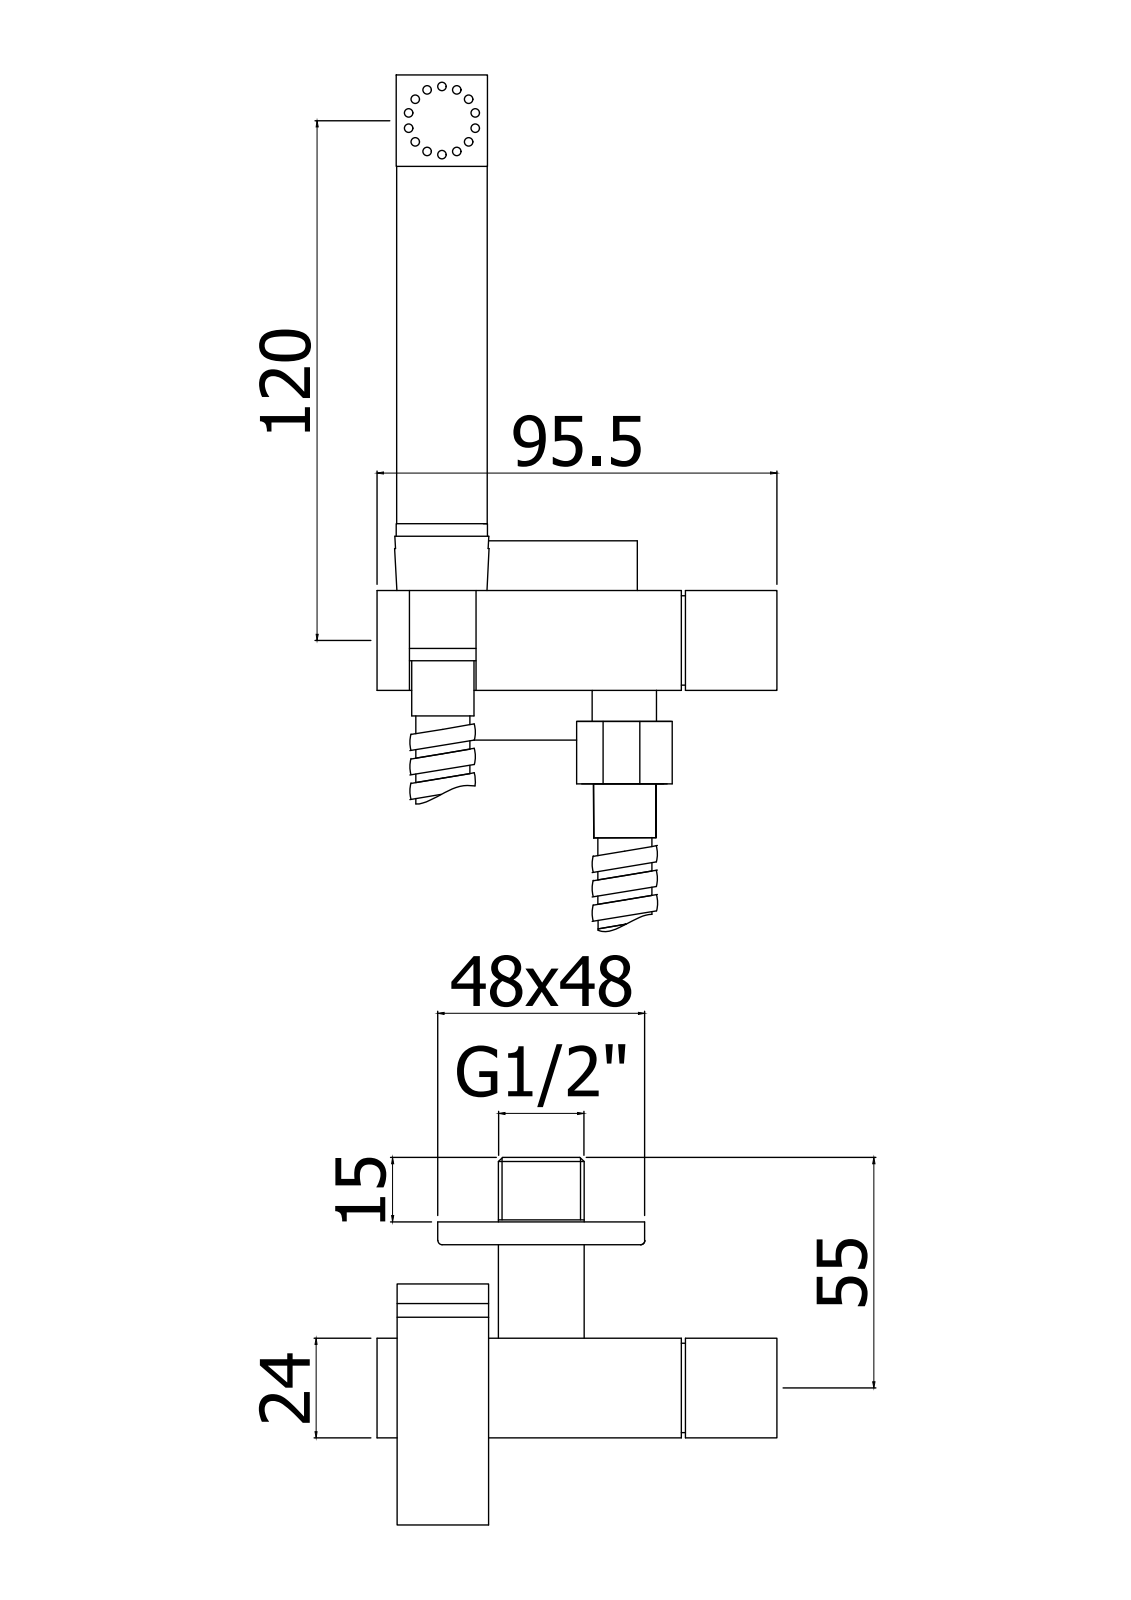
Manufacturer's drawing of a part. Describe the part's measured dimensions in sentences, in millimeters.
The part is named "ZDUP111CR". Its 3-D file was written by "CREO PARAMETRIC BY PTC INC, 2020044 (CONFIG_CONTROL_DESIGN)". It is 1 solid with 460 faces: 114 planar, 220 cylindrical and 126 other. Overall it measures 371 by 95.5 by 67.45 millimeters. Its volume is 171 674 cubic millimeters and its surface area 72 919 square millimeters. Round holes: 12 of diameter 1.2, 1 of diameter 10, 1 of diameter 15.5, 1 of diameter 20.2, 1 of diameter 22. Round bosses or shafts: 2 of diameter 15, 2 of diameter 14.5, 1 of diameter 21.5, 1 of diameter 21, 1 of diameter 20.5, 1 of diameter 20. Partial cylindrical surfaces (rounded edges, fillets, slot ends): 8 of radius 0.5, 8 of radius 1, 1 of radius 8. The main face-to-face distances are 0.9, 20.9, 21.8, 24, 20, 0.5, 1, 21, 21.9, 22. The hole center spacings are 6.25, 10.83, 3.23, 8.84, 12.07, 3.24, 12.08, 6.26.
